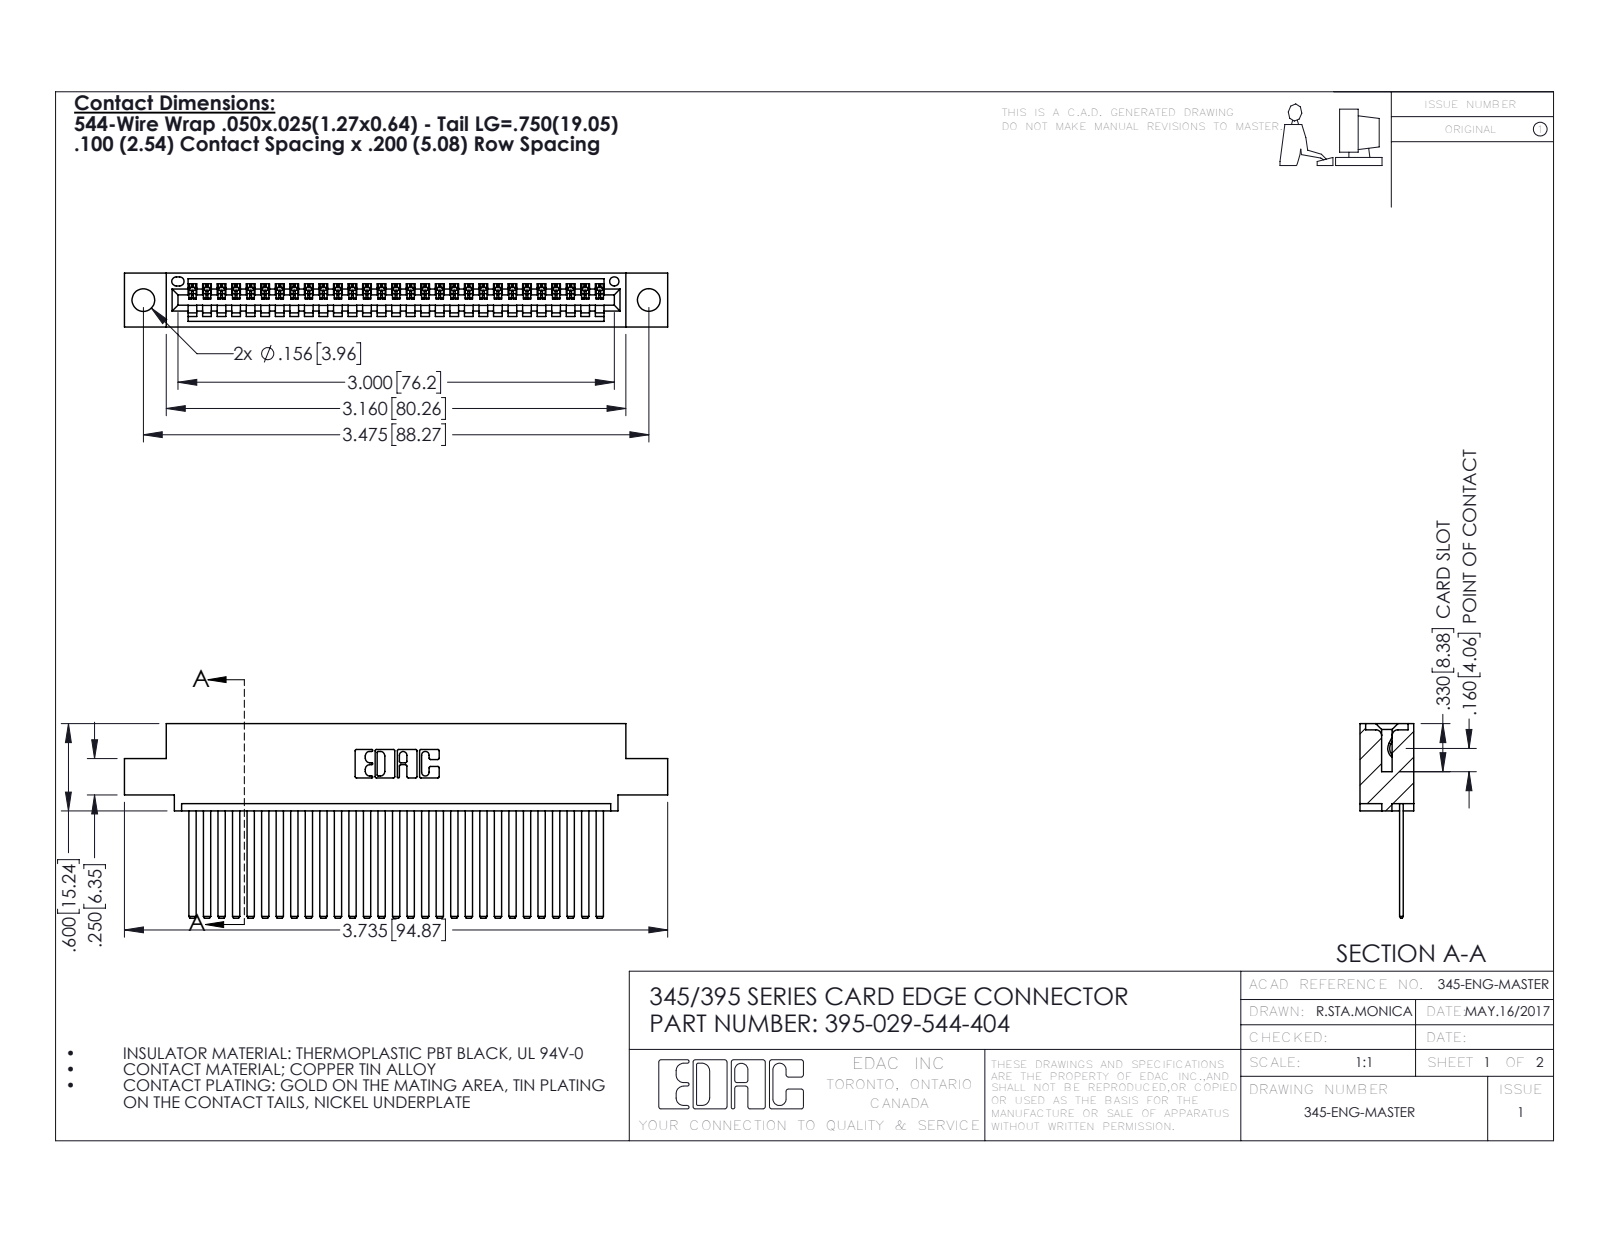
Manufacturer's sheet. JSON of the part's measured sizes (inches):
{"part_name": "345 Part_0.110 Offset - 0.156 Dia-TH; 345-292-001_345-293-144; 395-029-544-404", "step_written_by": "SolidWorks 2016 (CONFIG_CONTROL_DESIGN)", "units": "inches", "bodies": {"solids": 30, "faces": 1638, "planar": 1128, "cylindrical": 510, "other": 0}, "overall_size": [3.735, 1.337, 0.37], "volume_in3": 0.554, "surface_area_in2": 19.82, "round_holes": [[0.156, 2], [0.064, 1]], "partial_cylinders_radius": [[0.006, 58], [0.01, 22], [0.007, 6], [0.031, 6], [0.026, 3], [0.031, 2], [0.04, 2], [0.014, 1]], "face_to_face_distances": [0.072, 0.298, 0.098, 0.025, 0.272, 0.37, 0.2, 0.225, 0.149, 0.072], "hole_center_spacings": [0.27, 3.24, 3.475]}
